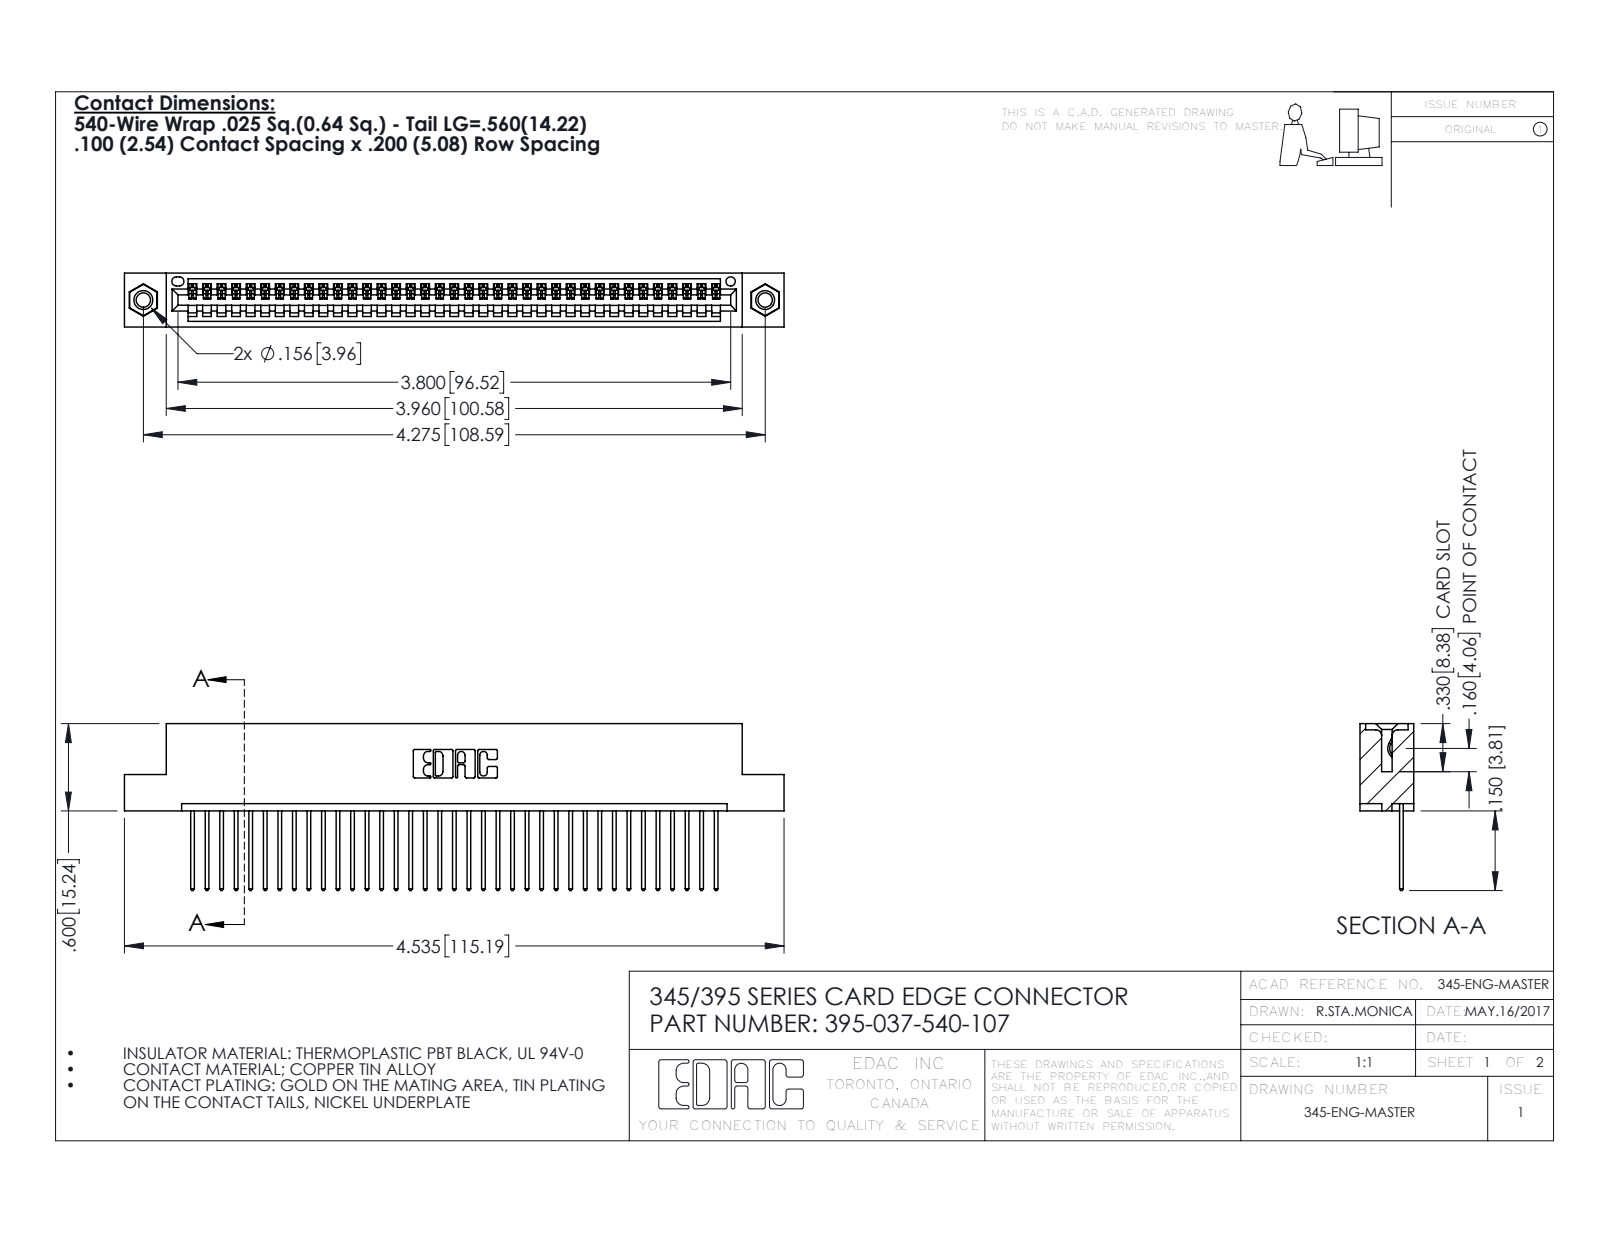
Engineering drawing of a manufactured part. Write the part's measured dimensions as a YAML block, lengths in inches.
part_name: "345-250-001_345-250-005-103; 345 Part_Flush Mounting Lugs - 0.156 Dia-TI; 395-037-540-107; 345-292-001_345-293-140"
step_written_by: "SolidWorks 2016 (CONFIG_CONTROL_DESIGN)"
units: inches
bodies: {solids: 40, faces: 2332, planar: 1592, cylindrical: 724, other: 16}
overall_size: [4.535, 1.147, 0.37]
volume: 0.667
surface_area: 23.03
round_holes:
  - {diameter: 0.098, count: 2}
  - {diameter: 0.125, count: 2}
  - {diameter: 0.156, count: 2}
  - {diameter: 0.064, count: 1}
round_bosses_or_shafts:
  - {diameter: 0.155, count: 2}
partial_cylinders:
  - {radius: 0.006, count: 74}
  - {radius: 0.01, count: 74}
  - {radius: 0.01, count: 22}
  - {radius: 0.007, count: 6}
  - {radius: 0.031, count: 6}
  - {radius: 0.026, count: 3}
  - {radius: 0.031, count: 2}
  - {radius: 0.04, count: 2}
face_to_face_distances: [0.072, 0.298, 0.2, 0.37, 0.098, 0.272, 0.025, 0.225, 0.149, 0.072]
hole_center_spacings: [0.27, 4.039, 4.275]
